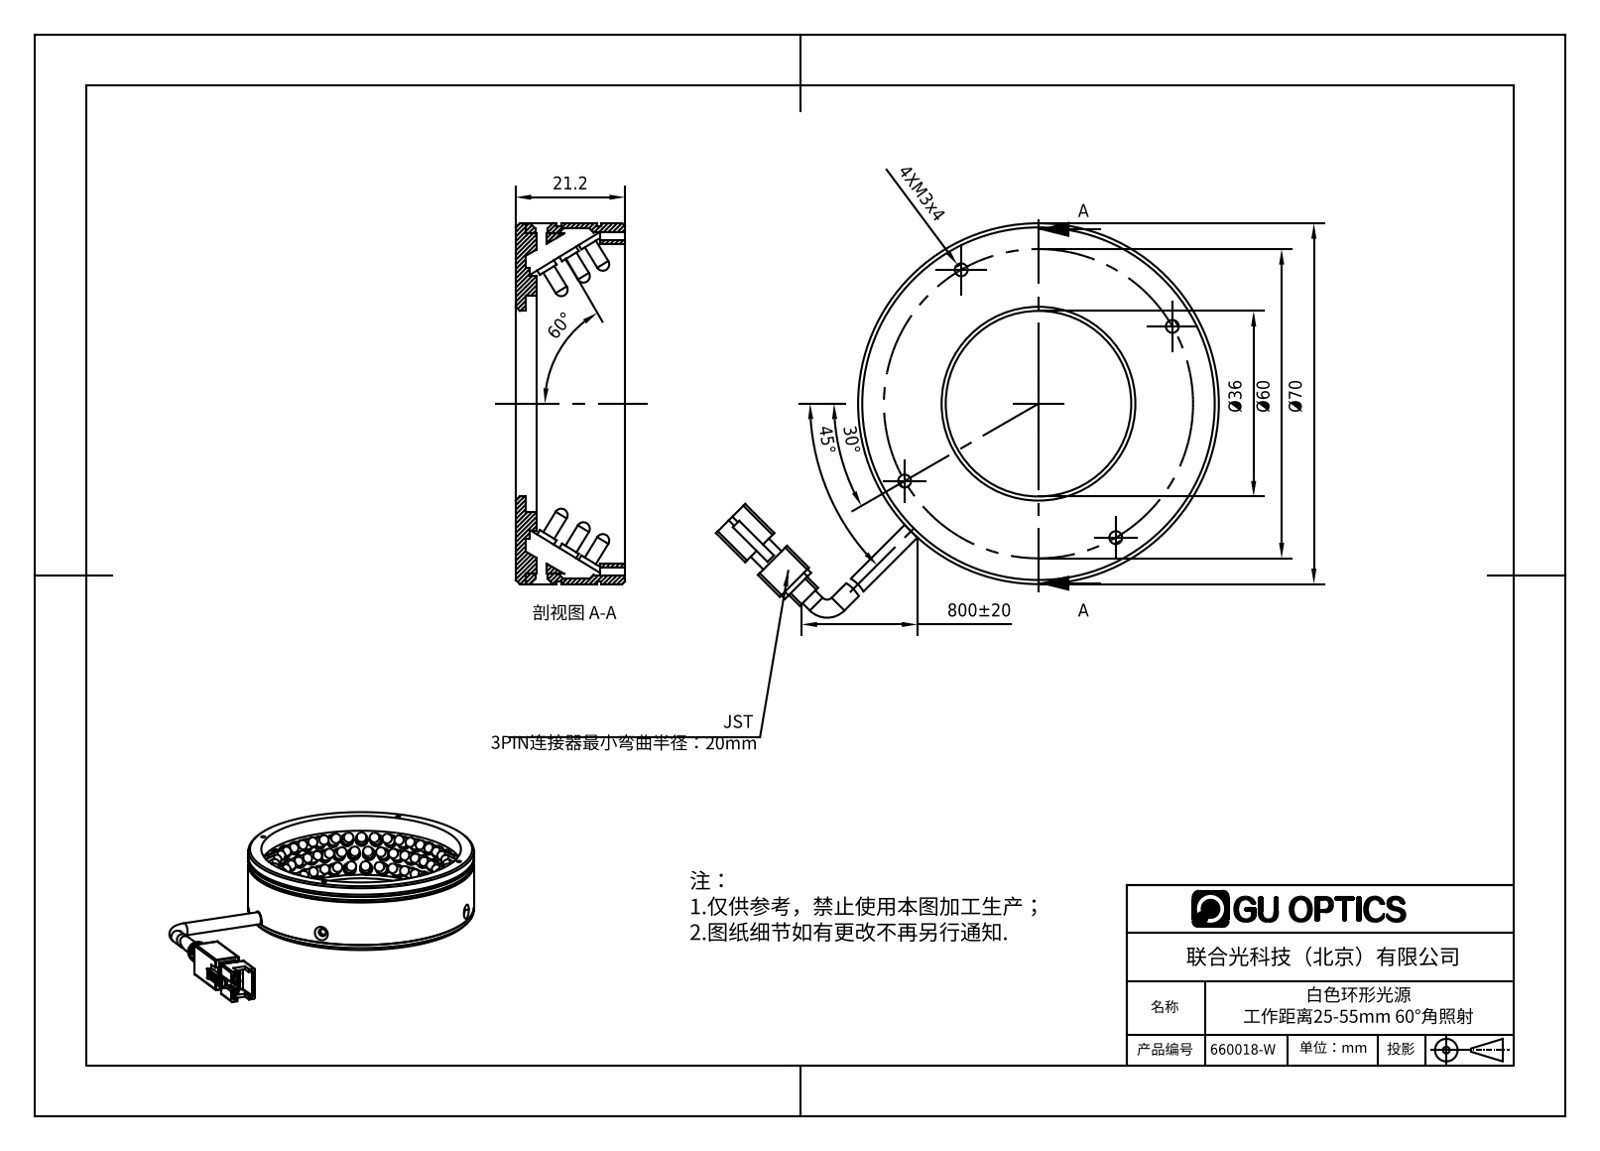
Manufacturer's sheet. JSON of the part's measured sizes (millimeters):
{"part_name": "660018-W", "step_written_by": "SolidWorks 2016 (AUTOMOTIVE_DESIGN)", "units": "millimeters", "bodies": {"solids": 118, "faces": 2275, "planar": 1503, "cylindrical": 596, "other": 176}, "overall_size": [122.68, 80.79, 22.65], "volume_mm3": 27288, "surface_area_mm2": 37585, "round_holes": [[1.25, 4], [2.5, 4], [3.8, 3], [2, 2], [2.4, 2], [36, 1], [42, 1], [62, 1], [66, 1], [68, 1]], "round_bosses_or_shafts": [[3.8, 112], [3, 112], [70, 1], [69, 1], [52.5, 1], [49.5, 1], [3.5, 1]], "partial_cylinders_radius": [[0.1, 15], [0.2, 13], [0.4, 12], [0.3, 1], [0.68, 1], [1.4, 1], [1.65, 1], [4.5, 1]], "face_to_face_distances": [2, 1, 21.2, 19.2, 0.5, 2.7, 0.7, 18.5, 1.5, 13.6], "hole_center_spacings": [16.36, 30, 31.32, 32.5, 42.43, 45.96, 54.14, 60.37]}
